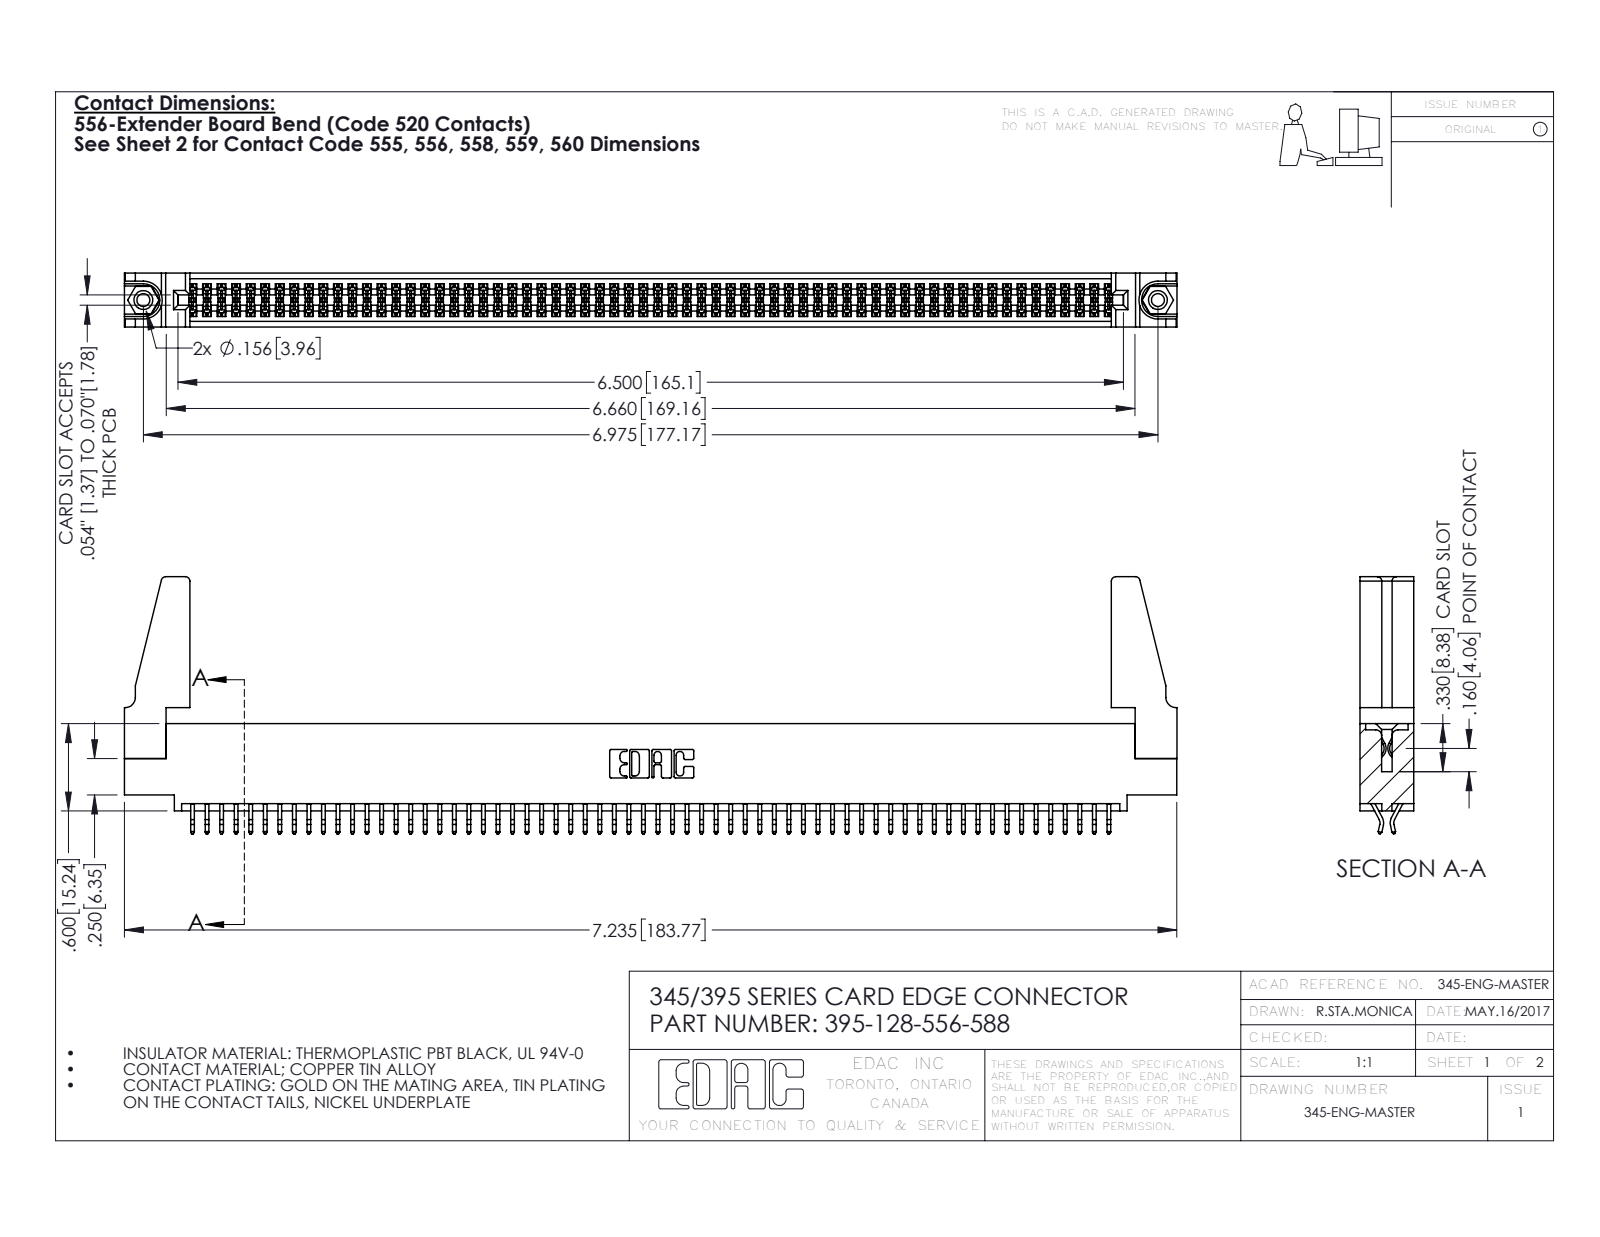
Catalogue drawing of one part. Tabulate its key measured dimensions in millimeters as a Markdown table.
| quantity | value |
| --- | --- |
| part name | 345-250-001_345-250-001-102; 395-128-556-588; 345 Part_0.110 Offset - 0.156 Dia-TH; 345-292-001_556 Tail (+1 more) |
| STEP written by | SolidWorks 2016 (CONFIG_CONTROL_DESIGN) |
| units | millimeters |
| bodies | 133 solids, 7422 faces (4892 planar, 2514 cylindrical, 16 other) |
| overall size | 183.8 × 44.9 × 9.4 |
| volume | 21 240 mm³ |
| surface area | 30 100 mm² |
| round holes (diameter × count) | 2.3 × 2, 3.2 × 2, 4 × 2, 1.6 × 1 |
| round bosses / shafts (diameter × count) | 3.9 × 2 |
| partial cylindrical surfaces (radius × count) | 0.2 × 192, 0.3 × 22, 0.8 × 8, 0.2 × 6, 0.8 × 6, 0.7 × 3, 0.3 × 2, 0.4 × 2 |
| main face-to-face distances | 1.8, 7.6, 9.4, 0.6, 2.5, 6.9, 5.1, 5.7, 4.4, 3.8 |
| hole center spacings | 6.9, 171.2, 177.2 |
